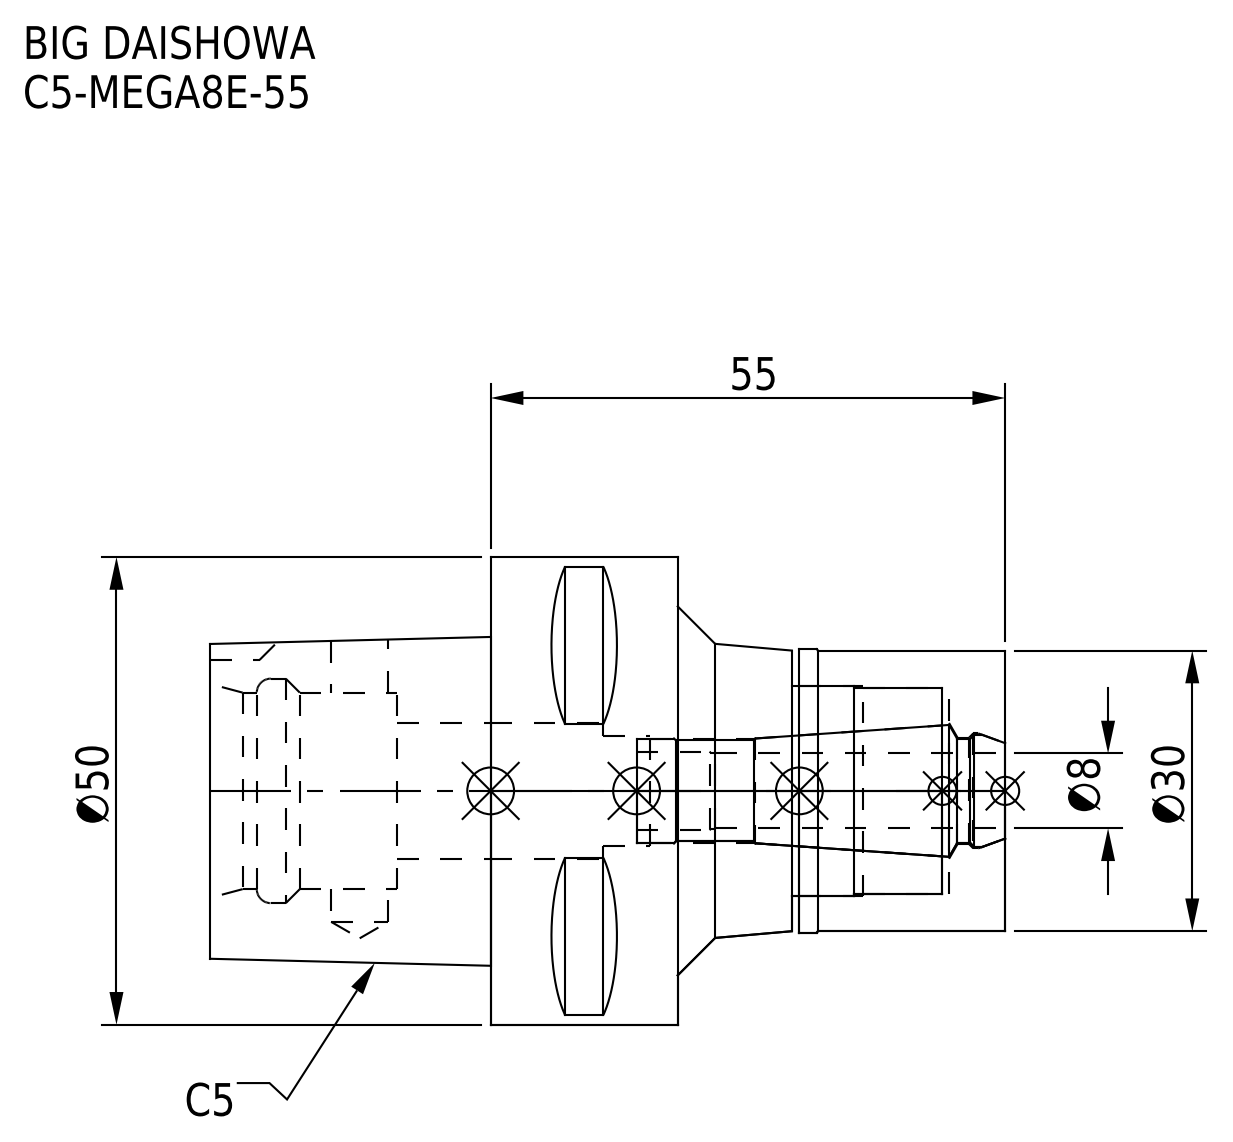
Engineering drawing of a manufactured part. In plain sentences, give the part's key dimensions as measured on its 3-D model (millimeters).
The part is named "C5-MEGA8E-55_1.stp; C5-MEGA8E-55-080.stp; C5-MEGA8E-55; C5-MEGA8E-55-080_ASM.stp (+3 more)". Its 3-D file was written by "SolidWorks 2019 (CONFIG_CONTROL_DESIGN)". It is 2 solids with 94 faces: 35 planar, 35 cylindrical and 24 other. Overall it measures 85 by 50 by 50 millimeters. Its volume is 75 332 cubic millimeters and its surface area 20 777 square millimeters. Round holes: 1 of diameter 6.1, 1 of diameter 11.2, 1 of diameter 11.4, 1 of diameter 11.8, 1 of diameter 12.3, 1 of diameter 14.5, 1 of diameter 21, 1 of diameter 22, 1 of diameter 22.5, 1 of diameter 24. Round bosses or shafts: 1 of diameter 50, 1 of diameter 30.3, 1 of diameter 30. Partial cylindrical surfaces (rounded edges, fillets, slot ends): 1 of radius 4. The main face-to-face distances are 20, 35, 55, 30, 85, 50, 22, 13, 33, 63.
